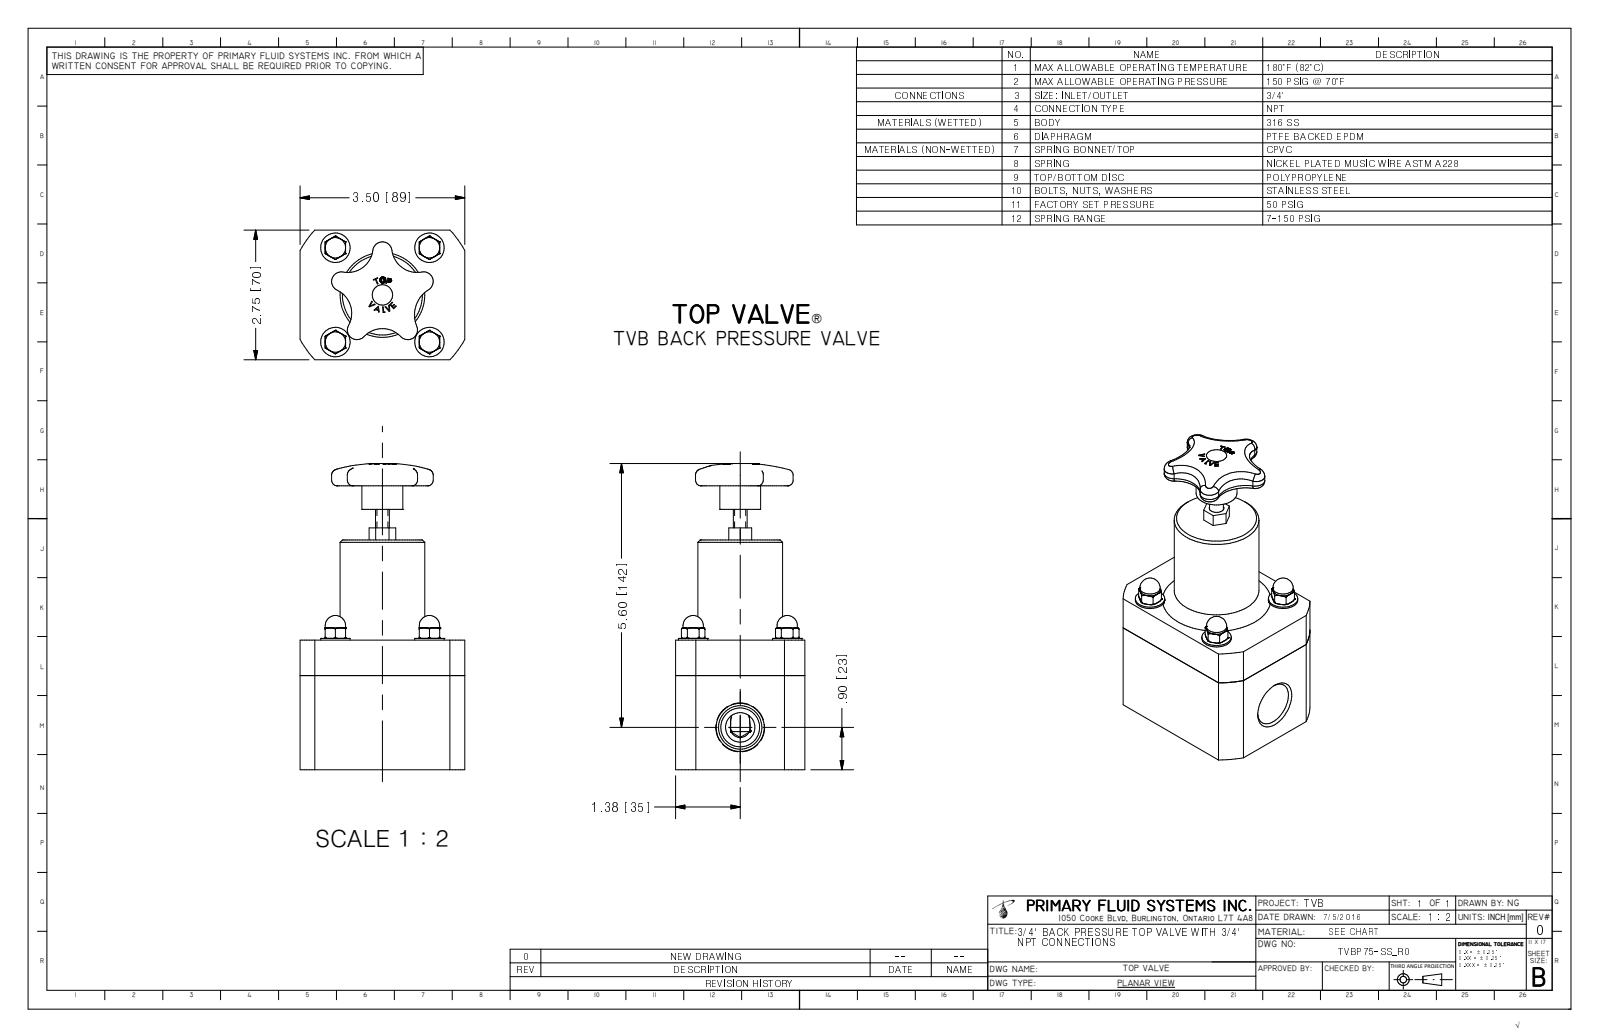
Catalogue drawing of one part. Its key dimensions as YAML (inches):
part_name: "TVBP75-SS-R0"
step_written_by: "Autodesk Inventor 2009 (AUTOMOTIVE_DESIGN)"
units: inches
bodies: {solids: 1, faces: 337, planar: 144, cylindrical: 45, other: 148}
overall_size: [6.497, 3.5, 2.75]
volume: 31.73
surface_area: 82.43
round_holes:
  - {diameter: 0.175, count: 4}
  - {diameter: 0.922, count: 1}
round_bosses_or_shafts:
  - {diameter: 0.625, count: 4}
  - {diameter: 0.433, count: 4}
  - {diameter: 0.375, count: 4}
  - {diameter: 1.8, count: 1}
  - {diameter: 0.87, count: 1}
  - {diameter: 0.293, count: 1}
partial_cylinders:
  - {radius: 0.085, count: 5}
  - {radius: 0.205, count: 5}
  - {radius: 0.536, count: 4}
  - {radius: 0.656, count: 4}
  - {radius: 0.625, count: 1}
  - {radius: 0.745, count: 1}
  - {radius: 1.988, count: 1}
face_to_face_distances: [2.75, 2.75, 3.5, 4.875, 2.125, 0.75, 2, 0.433, 2.786, 0.036]
hole_center_spacings: [2, 2.828]
